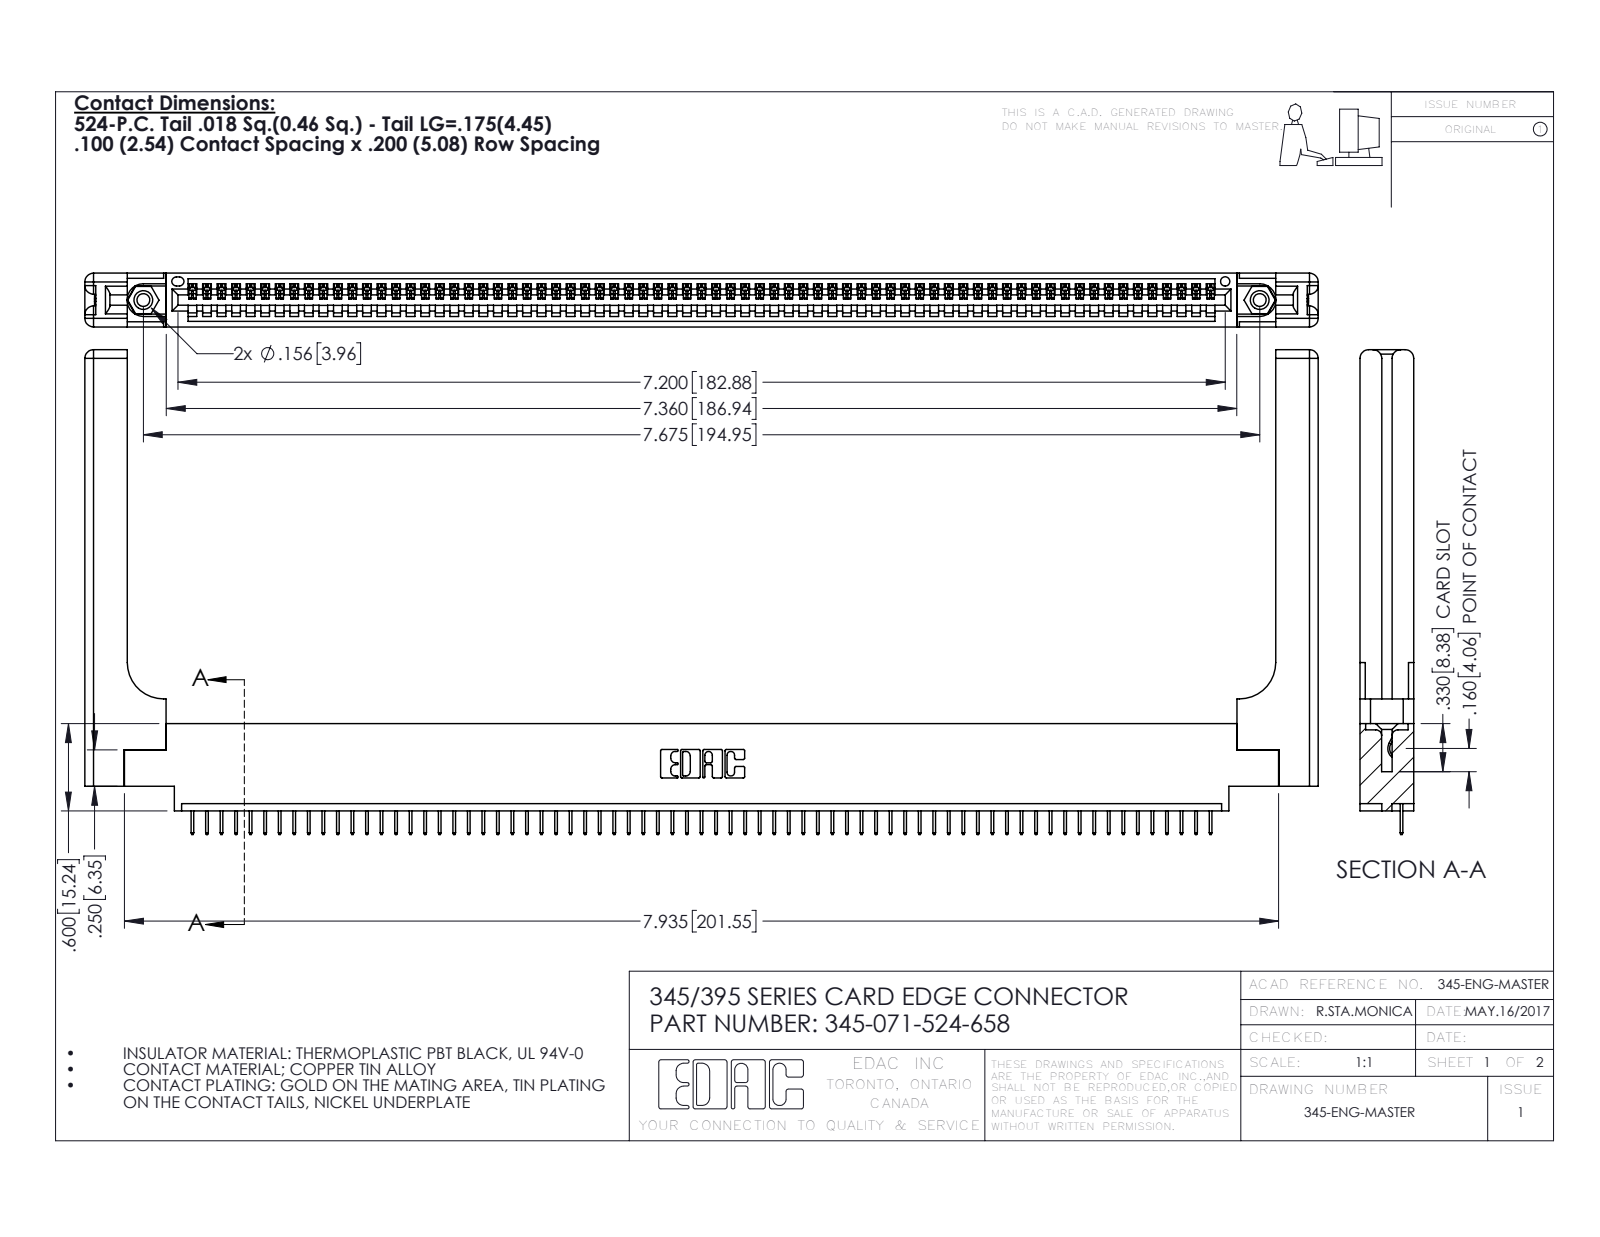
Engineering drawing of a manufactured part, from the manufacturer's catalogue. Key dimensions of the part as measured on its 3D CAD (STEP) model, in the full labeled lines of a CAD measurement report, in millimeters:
Part name (STEP PRODUCT): 345-220-058_345-220-058; 345-250-001_345-250-001-102; 345 Part_0.170 Offset - 0.156 Dia-TH; 345-292-001_345-293-124 (+1 more)
STEP written by: SolidWorks 2016 (CONFIG_CONTROL_DESIGN)
Units: millimetres
Bodies: 76 solids, 4788 faces (3498 planar, 1230 cylindrical, 60 other)
Overall size (bounding box): 215.4 × 84.6 × 9.4
Volume: 28 810 mm³ · Surface area: 31 900 mm²
Round holes (diameter × count): ⌀2.3 ×2, ⌀3.2 ×2, ⌀4 ×2, ⌀1.6 ×1
Round bosses / shafts (diameter × count): ⌀3.9 ×2
Partial cylindrical surfaces — rounded edges, fillets, slot ends (radius × count): R0.2 ×142, R0.3 ×22, R1.5 ×16, R0.2 ×6, R0.8 ×6, R0.7 ×3, R0.8 ×2, R0.8 ×2
Main face-to-face distances: 1.8, 9.4, 7.6, 2.5, 6.9, 0.6, 5.1, 5.7, 3.8, 3.8
Hole centre spacings: 6.9, 189, 194.9
